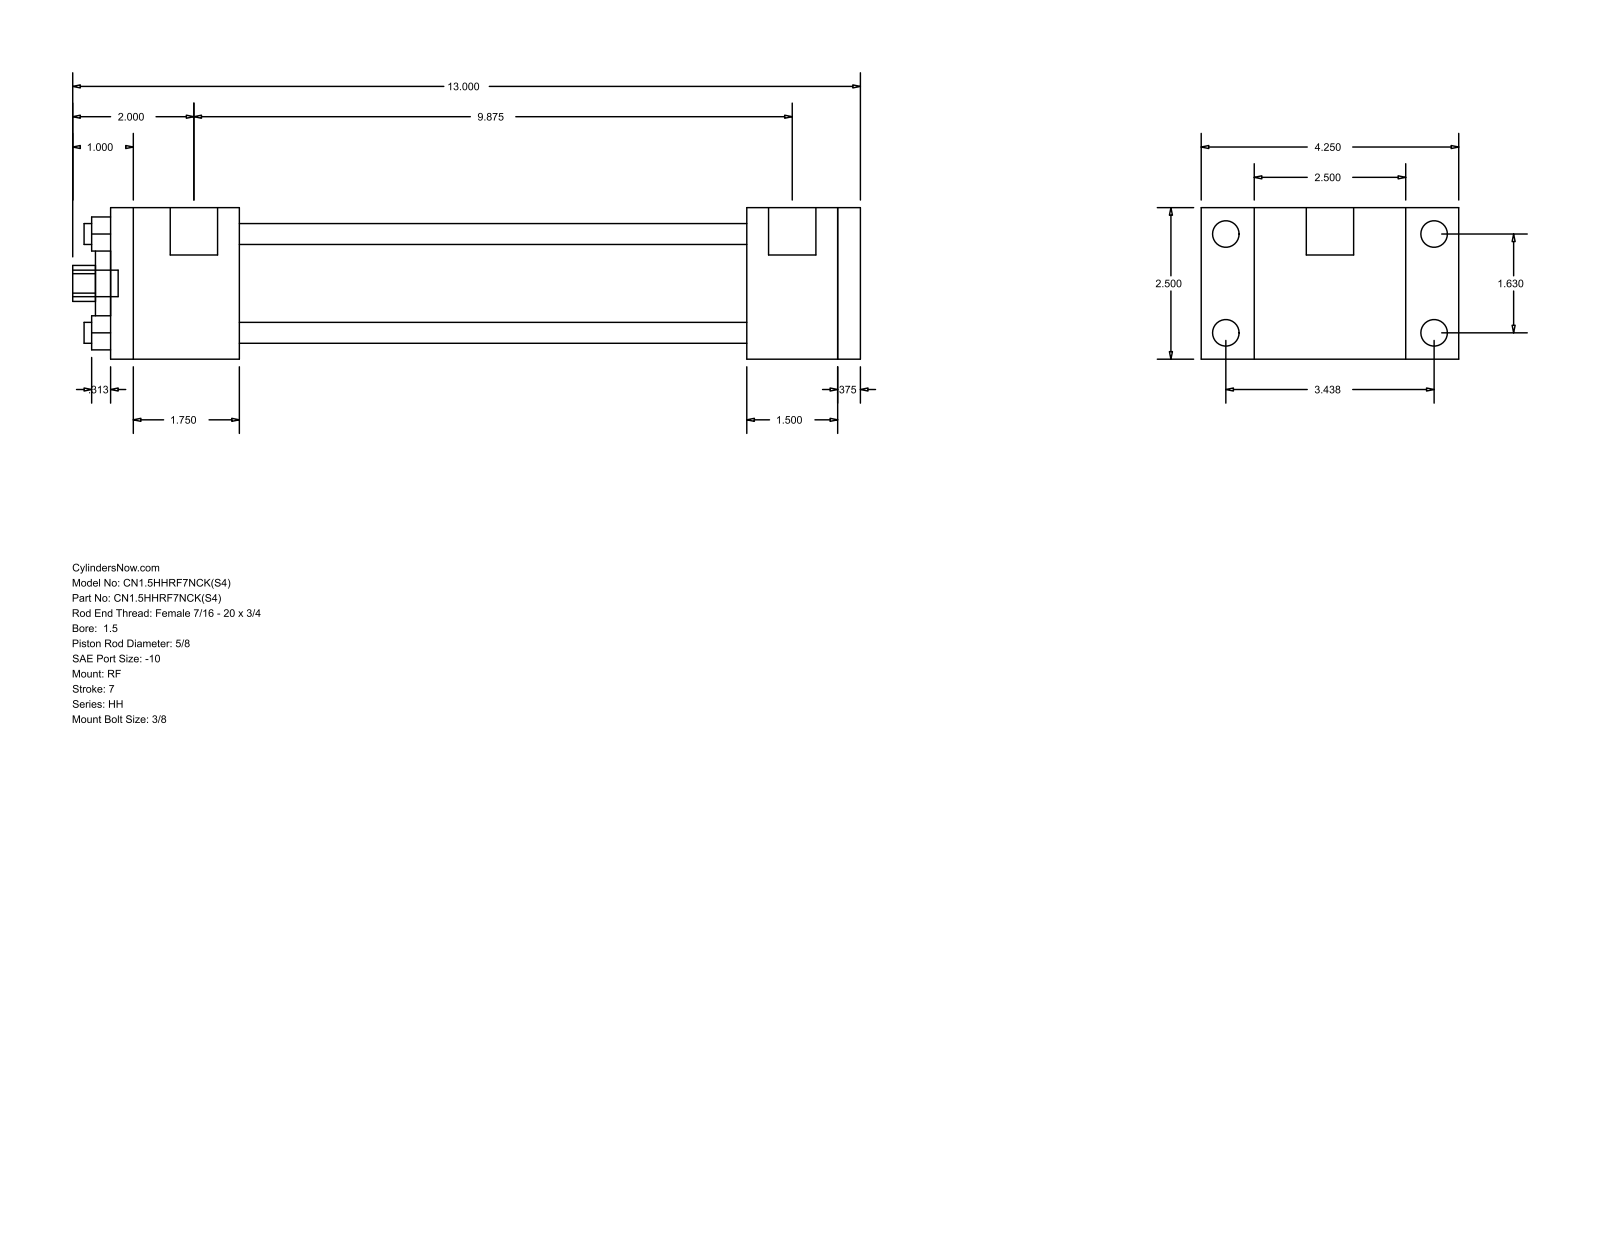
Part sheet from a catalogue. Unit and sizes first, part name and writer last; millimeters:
Units: millimetres
Overall size (bounding box): 330.2 × 107.95 × 63.5
Round holes (diameter × count): ⌀8.76 ×4, ⌀15.88 ×1, ⌀28.57 ×1, ⌀44.45 ×1
Round bosses / shafts (diameter × count): ⌀11.13 ×4, ⌀5.56 ×4, ⌀19.84 ×2, ⌀11.11 ×1
Partial cylindrical surfaces — rounded edges, fillets, slot ends (radius × count): R7.54 ×1
Main face-to-face distances: 63.5, 314.32, 9.52, 304.8, 47.63, 53.97, 266.69, 212.72, 250.83, 260.35
Hole centre spacings: 29.27, 41.4, 58.55
Bodies: 0 solids, 92 faces (64 planar, 28 cylindrical, 0 other)
Part name (STEP PRODUCT): HH_RF__0150_0.625
STEP written by: GSSL Pune (CONFIG_CONTROL_DESIGN)
